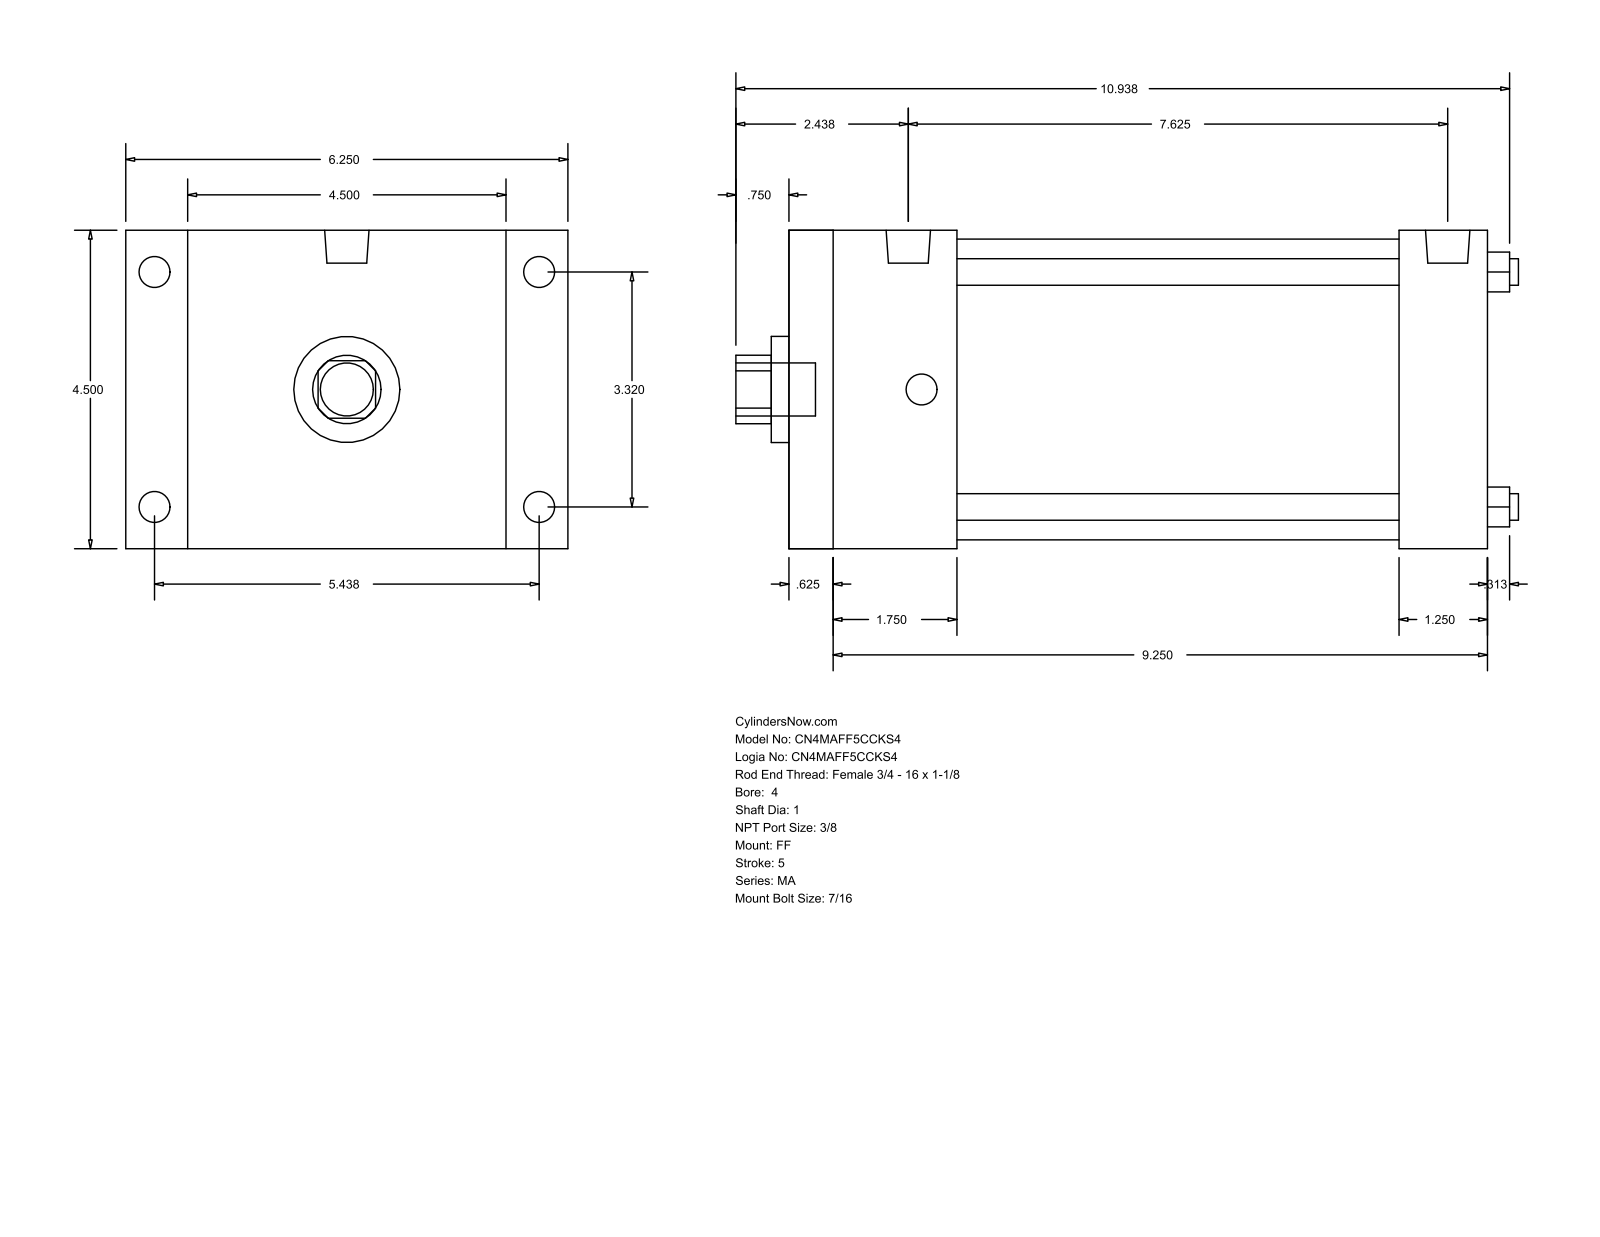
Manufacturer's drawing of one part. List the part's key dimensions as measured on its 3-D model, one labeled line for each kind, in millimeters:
Part name (STEP PRODUCT): MA_FF__0400_1
STEP written by: GSSL Pune (CONFIG_CONTROL_DESIGN)
Units: millimetres
Bodies: 0 solids, 92 faces (64 planar, 28 cylindrical, 0 other)
Overall size (bounding box): 280.99 × 158.75 × 114.3
Round holes (diameter × count): ⌀9.53 ×4, ⌀25.4 ×1, ⌀38.1 ×1, ⌀107.95 ×1
Round bosses / shafts (diameter × count): ⌀11.11 ×8, ⌀15.93 ×2, ⌀19.05 ×1
Partial cylindrical surfaces — rounded edges, fillets, slot ends (radius × count): R12.29 ×1
Main face-to-face distances: 114.3, 250.83, 15.87, 234.96, 22.23, 136.53, 219.07, 203.2, 31.76, 60.33
Hole centre spacings: 59.62, 84.32, 119.25
